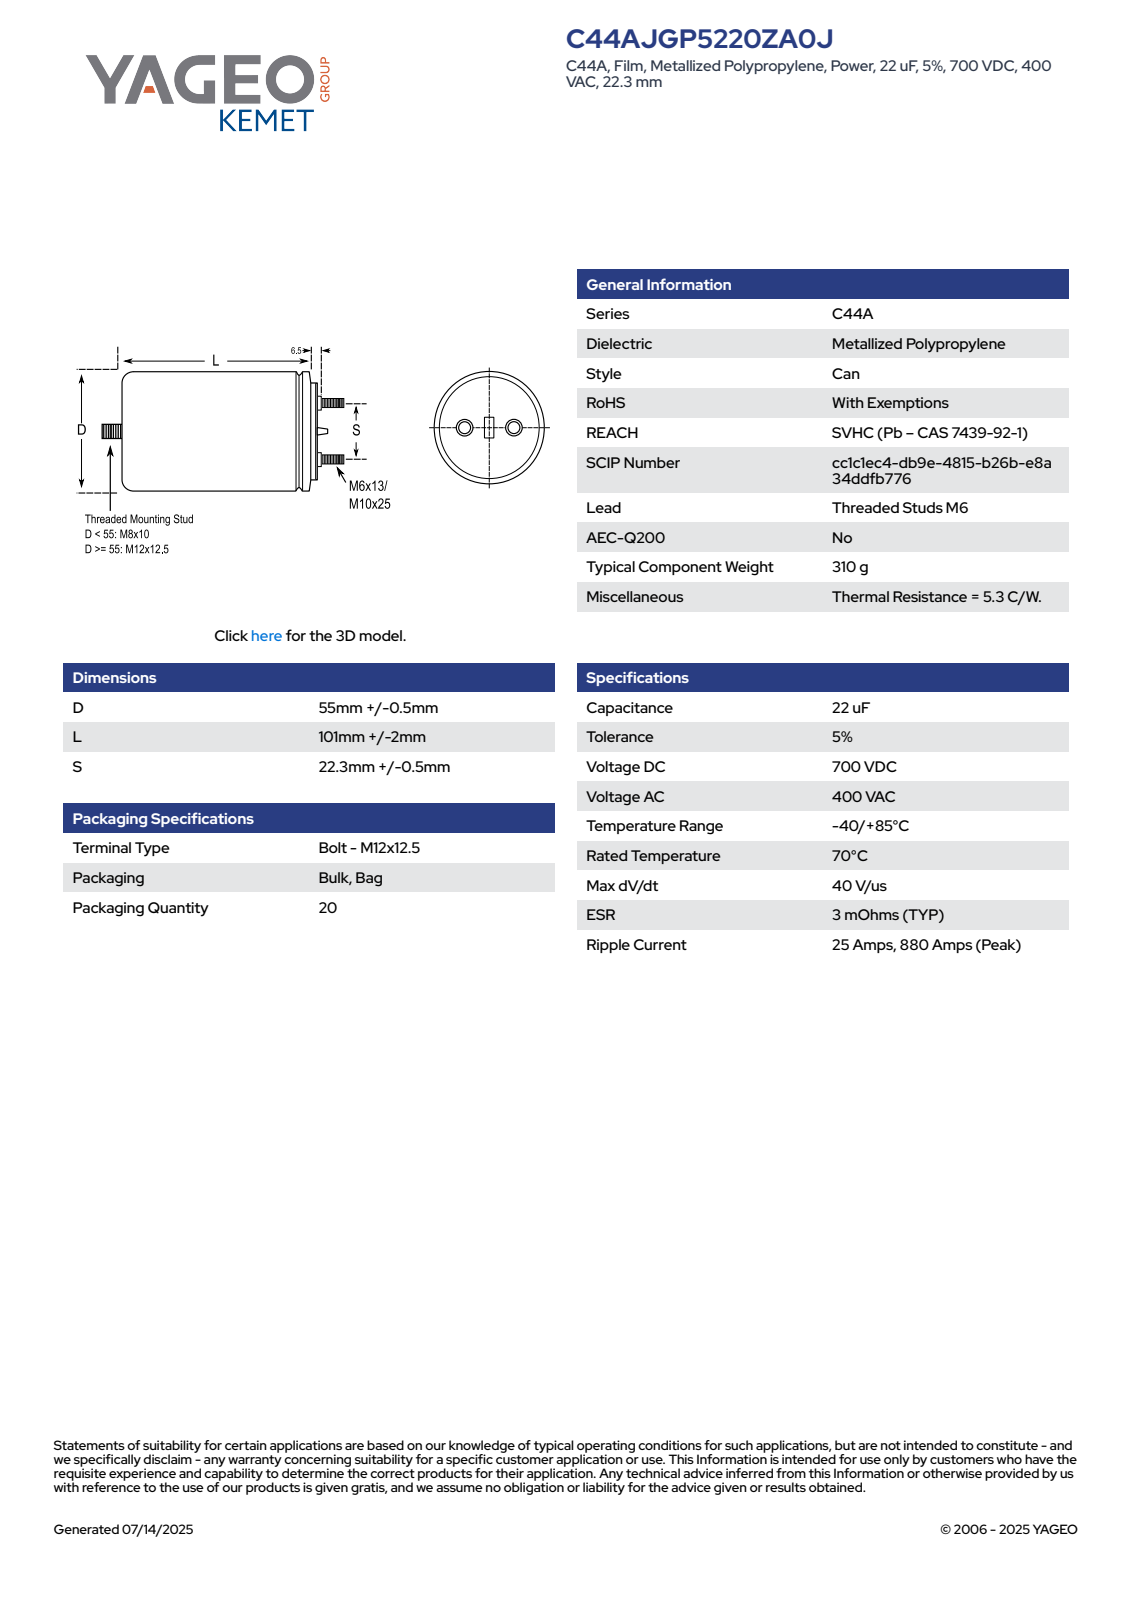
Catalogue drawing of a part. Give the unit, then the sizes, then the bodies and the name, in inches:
Units: inches
Overall size (bounding box): 5.315 × 2.185 × 2.185
Round bosses / shafts (diameter × count): ⌀0.354 ×2, ⌀0.236 ×2, ⌀2.185 ×1, ⌀1.714 ×1, ⌀0.472 ×1
Partial cylindrical surfaces — rounded edges, fillets, slot ends (radius × count): R1.092 ×1
Main face-to-face distances: 4.252, 0.492, 4.744, 4.803, 4.311, 0.059, 5.315, 4.823, 0.571, 0.512
Volume: 15.68 in³ · Surface area: 37.69 in²
Bodies: 1 solid, 102 faces (29 planar, 34 cylindrical, 39 other)
Part name (STEP PRODUCT): CFP_C44A_55X101_D55.5L103S22.3
STEP written by: SolidWorks 2014 (AUTOMOTIVE_DESIGN)
